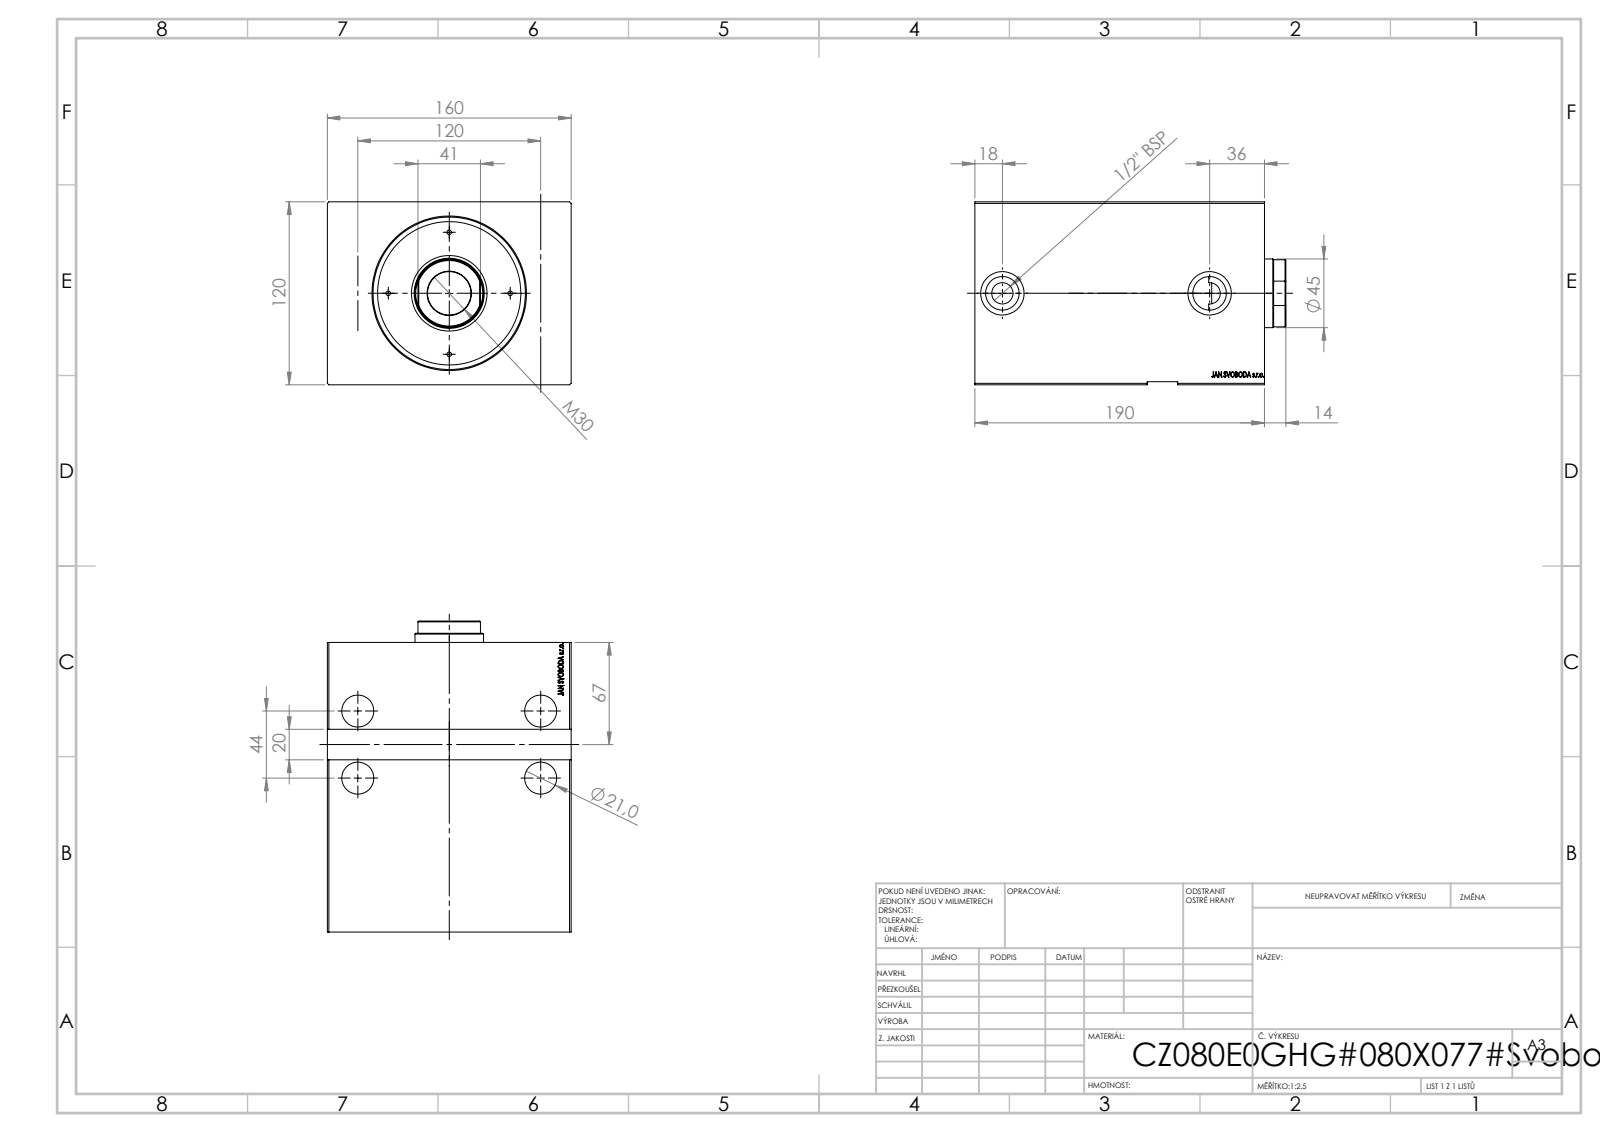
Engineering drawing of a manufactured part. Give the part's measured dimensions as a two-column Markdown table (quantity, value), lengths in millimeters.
| quantity | value |
| --- | --- |
| STEP written by | SolidWorks 2019 (CONFIG_CONTROL_DESIGN) |
| units | millimeters |
| bodies | 1 solid, 807 faces (395 planar, 30 cylindrical, 382 other) |
| overall size | 190 × 160 × 120 |
| volume | 2 596 000 mm³ |
| surface area | 217 919 mm² |
| round holes (diameter × count) | 21 × 4, 8 × 2, 22 × 2, 28.5 × 2, 14 × 1, 36 × 1, 80 × 1, 100 × 1 |
| partial cylindrical surfaces (radius × count) | 7 × 1 |
| main face-to-face distances | 120, 160, 190, 164.7, 25.3, 2, 118, 14, 150.7, 176 |
| hole center spacings | 44, 120, 127.81, 34.01, 54.82, 80.53, 86.01, 96.15 |
